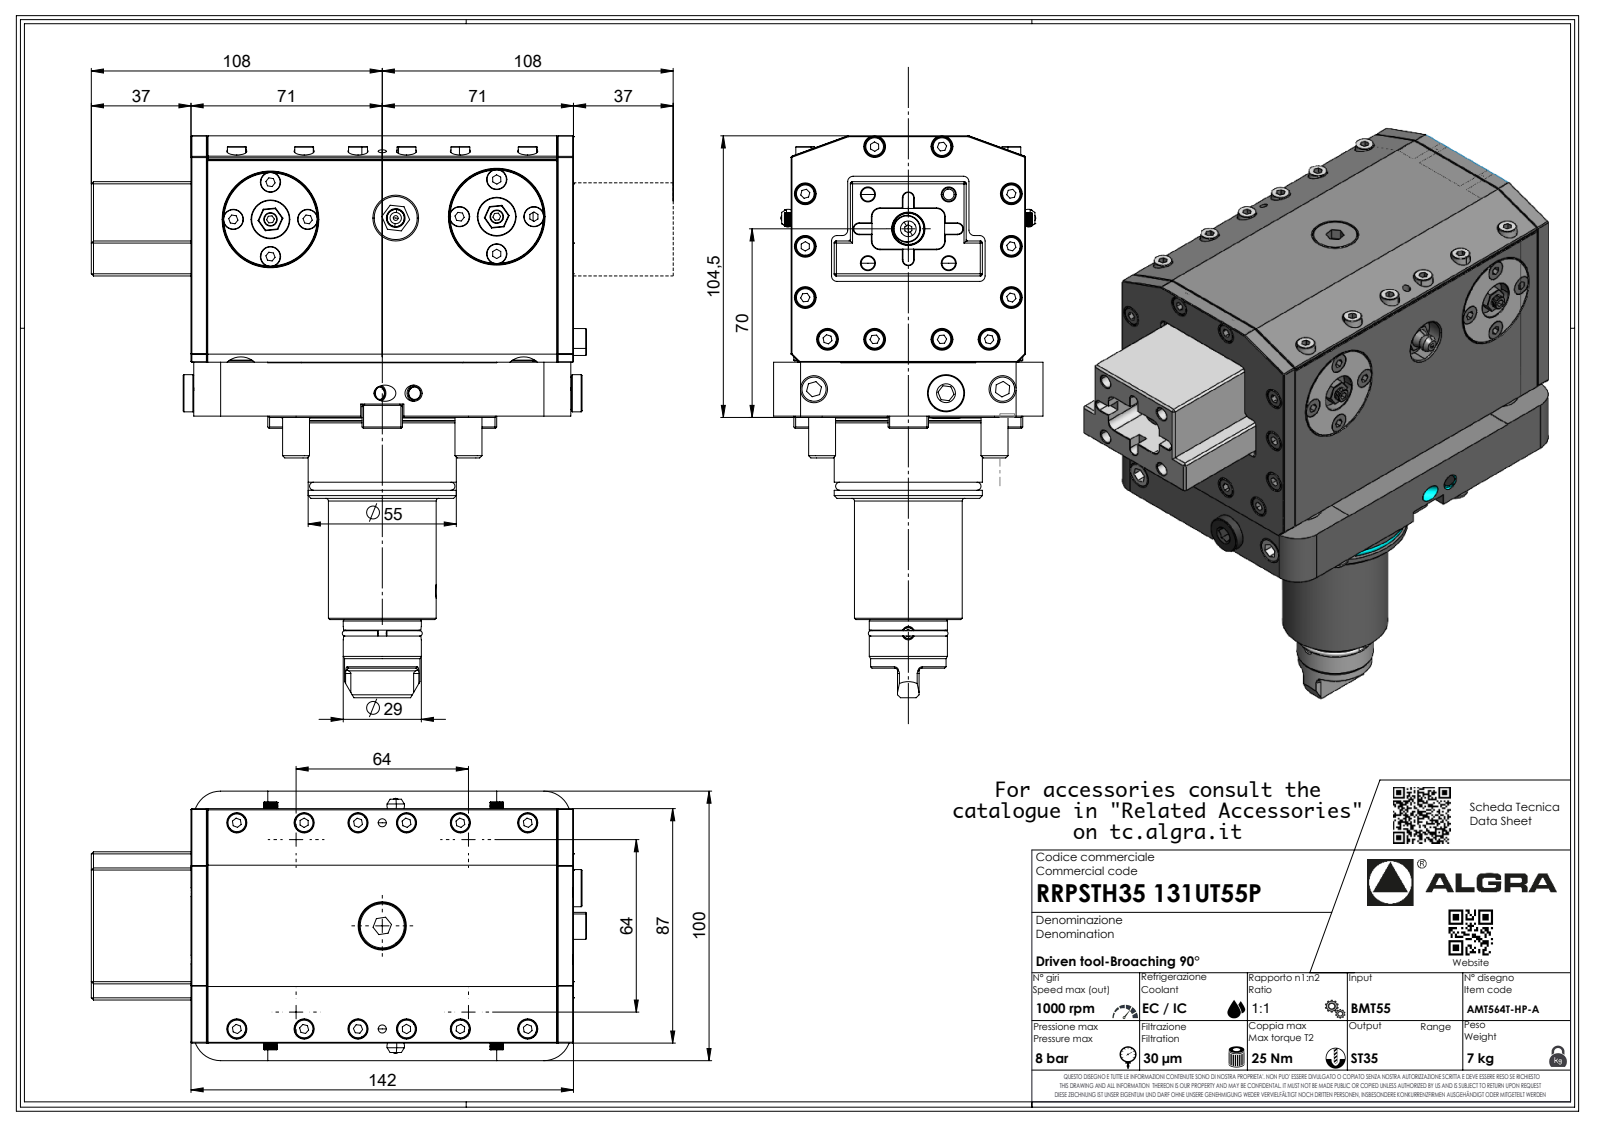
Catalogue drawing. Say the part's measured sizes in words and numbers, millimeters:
The part is named "RRPSTH35131UT55P". Its 3-D file was written by "SolidWorks 2023 (AUTOMOTIVE_DESIGN)". It is 1 solid with 898 faces: 485 planar, 147 cylindrical and 266 other. Overall it measures 208.5 by 183.82 by 100 millimeters. Its volume is 1 491 000 cubic millimeters and its surface area 112 610 square millimeters. Round holes: 4 of diameter 15, 2 of diameter 5, 1 of diameter 2.1. Round bosses or shafts: 12 of diameter 7, 4 of diameter 12, 2 of diameter 5, 1 of diameter 55, 1 of diameter 50.2, 1 of diameter 40, 1 of diameter 29, 1 of diameter 28. Partial cylindrical surfaces (rounded edges, fillets, slot ends): 13 of radius 2.5, 8 of radius 0.2, 8 of radius 0.5, 8 of radius 10, 7 of radius 0.33, 7 of radius 0.52, 7 of radius 3.7, 4 of radius 2. The main face-to-face distances are 87, 20, 19.8, 104, 84, 84.2, 142, 93.5, 6.5, 0.5. The hole center spacings are 70, 105, 126.19, 29.35, 53.12, 87.07, 97.68.
